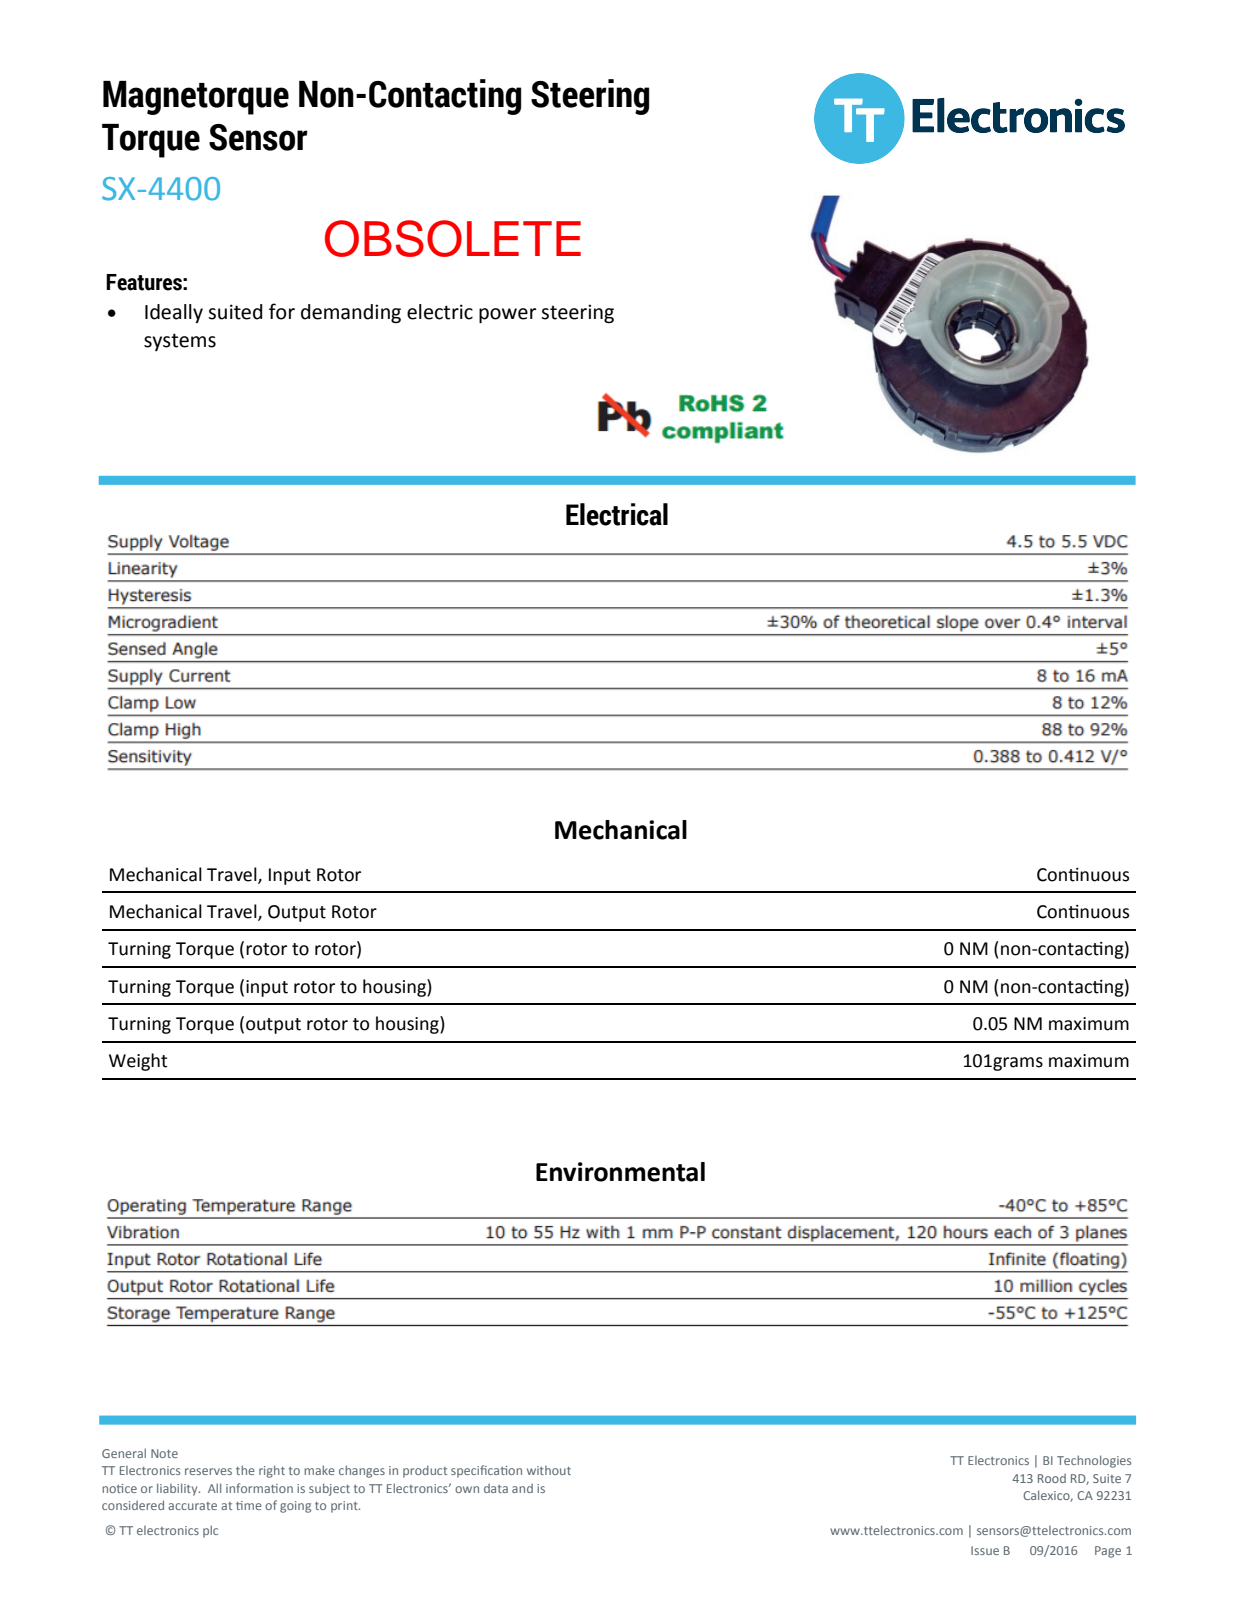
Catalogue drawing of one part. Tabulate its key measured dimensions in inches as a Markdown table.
| quantity | value |
| --- | --- |
| part name | 122-4400-50A_SW0003 |
| STEP written by | PRO/ENGINEER BY PARAMETRIC TECHNOLOGY CORPORATION, 2012060 (CONFIG_CONTROL_DESIGN) |
| units | inches |
| bodies | 1 solid, 2714 faces (1840 planar, 387 cylindrical, 487 other) |
| overall size | 15.225 × 3.206 × 0.942 |
| volume | 7.605 in³ |
| surface area | 64.85 in² |
| round holes (diameter × count) | 1.299 × 1 |
| round bosses / shafts (diameter × count) | 0.063 × 2, 3.102 × 1, 0.35 × 1 |
| partial cylindrical surfaces (radius × count) | 0.039 × 34, 0.01 × 14, 0.008 × 12, 0.059 × 7, 0.02 × 3, 0.031 × 3, 0.004 × 2, 0.006 × 2 |
| main face-to-face distances | 0.86, 0.039, 0.9, 0.05, 0.034, 0.109, 0.224, 0.185, 0.675, 0.09 |
